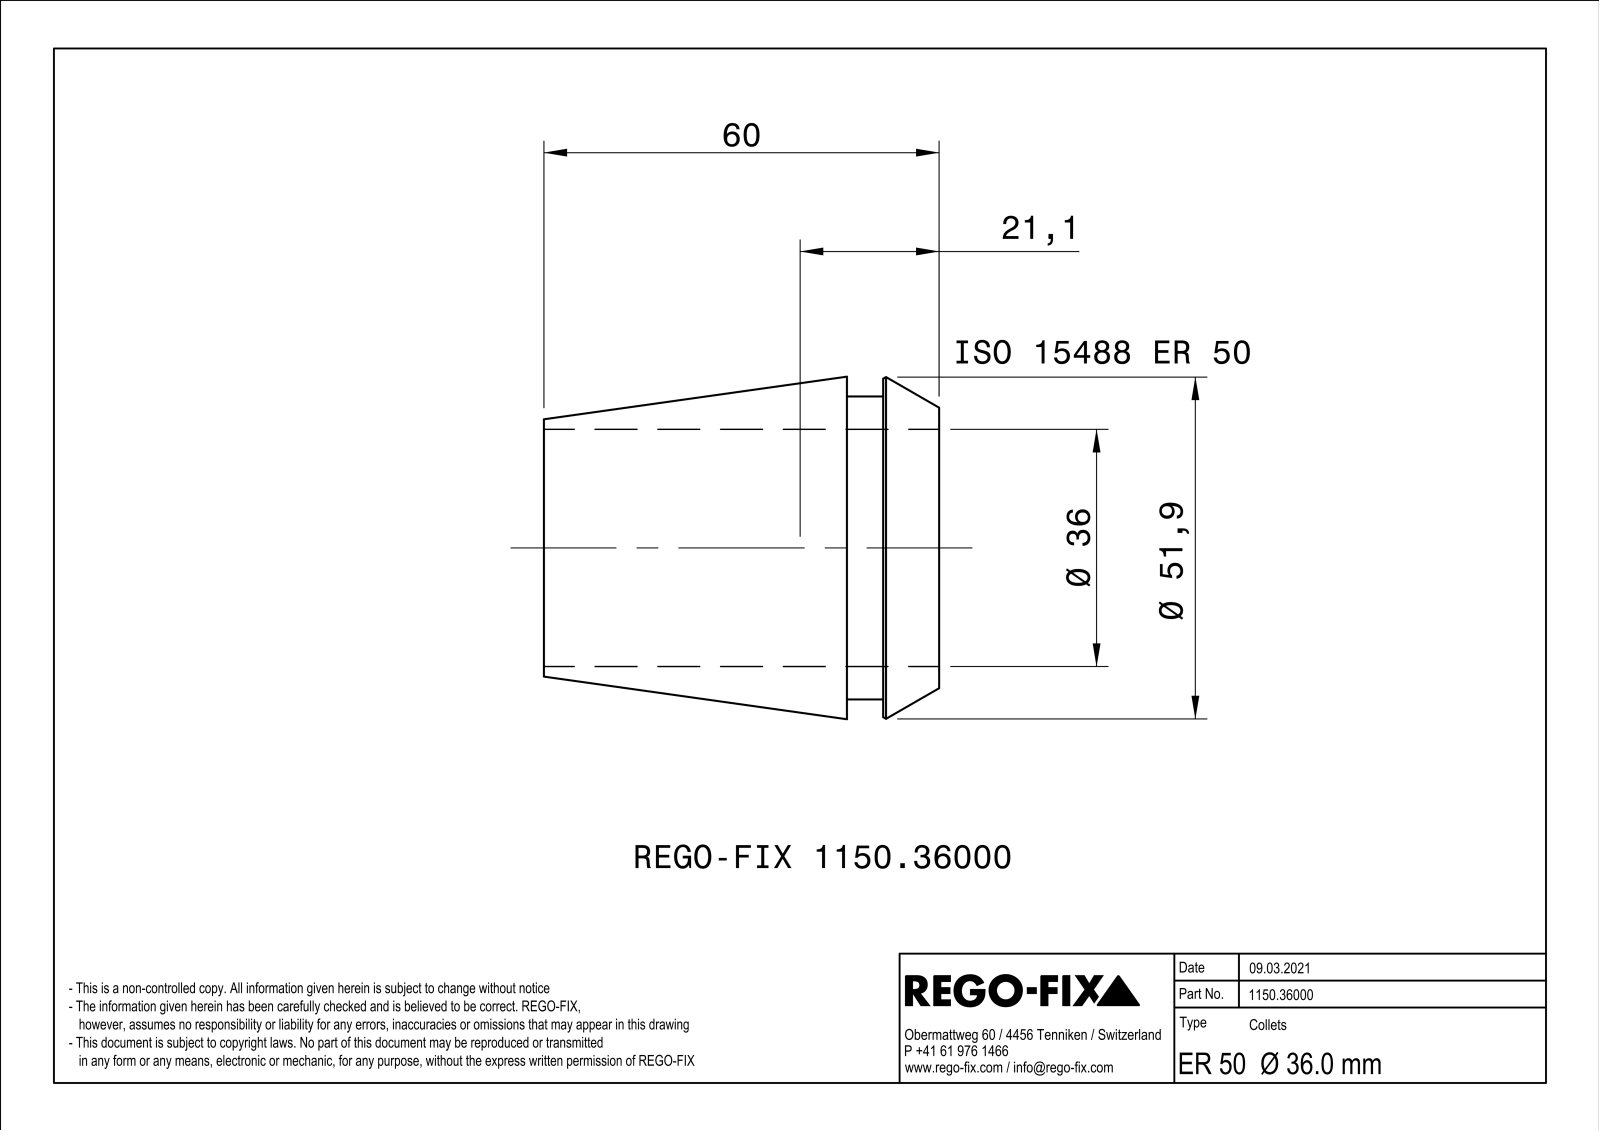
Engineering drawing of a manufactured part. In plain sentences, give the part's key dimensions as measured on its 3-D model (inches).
The part is named "NOCUT". Its 3-D file was written by "SIEMENS PLM Software Solid Edge ST10 (AUTOMOTIVE_DESIGN)". It is 1 solid with 177 faces: 88 planar, 9 cylindrical and 80 other. Overall it measures 2.362 by 2.047 by 2.047 inches. Its volume is 2.1 cubic inches and its surface area 36.73 square inches. Round holes: 1 of diameter 1.417. Round bosses or shafts: 1 of diameter 1.811. The main face-to-face distances are 0.039, 0.551, 0.335, 0.217, 2.362, 2.028, 1.811, 0.354, 2.008, 0.02.
